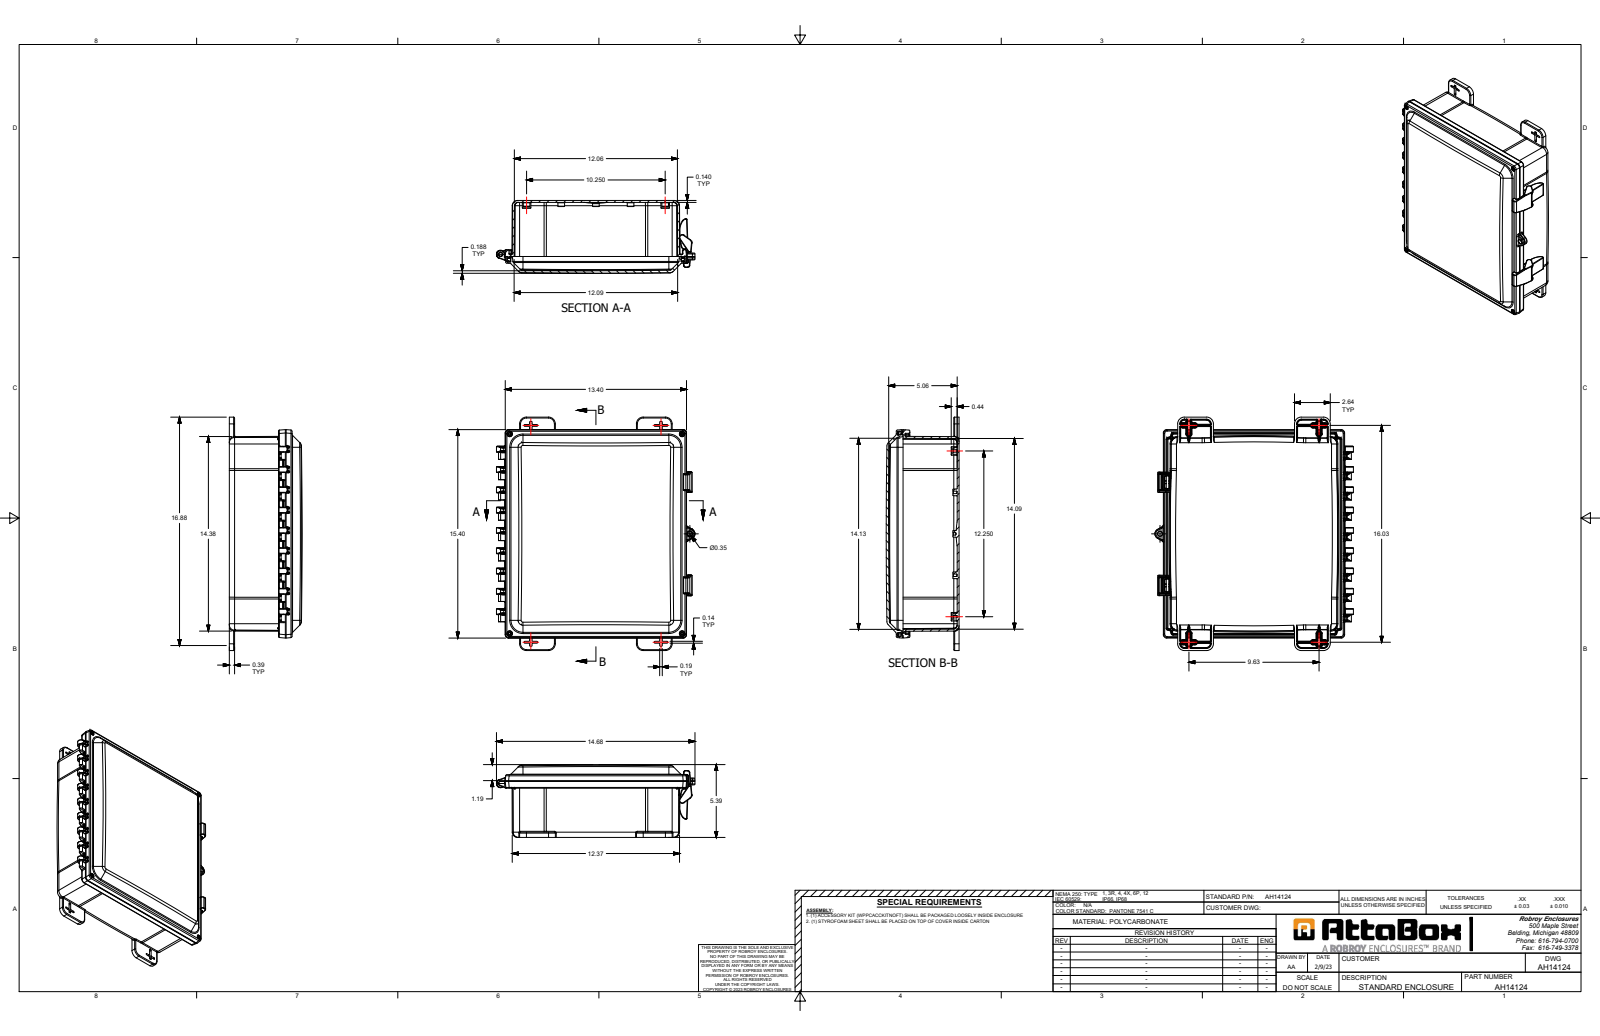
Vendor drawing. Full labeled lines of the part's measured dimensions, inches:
Part name (STEP PRODUCT): AH14124C
STEP written by: SolidWorks 2023 (AUTOMOTIVE_DESIGN)
Units: inches
Bodies: 6 solids, 1306 faces (449 planar, 451 cylindrical, 406 other)
Overall size (bounding box): 17.25 × 14.676 × 5.388
Volume: 123.2 in³ · Surface area: 1 453 in²
Round holes (diameter × count): ⌀0.187 ×21, ⌀0.195 ×4, ⌀0.25 ×4, ⌀0.296 ×4, ⌀0.39 ×4, ⌀0.327 ×1, ⌀0.375 ×1, ⌀0.45 ×1
Round bosses / shafts (diameter × count): ⌀0.487 ×21, ⌀0.625 ×4, ⌀0.2 ×2, ⌀0.313 ×1
Partial cylindrical surfaces — rounded edges, fillets, slot ends (radius × count): R0.035 ×194, R0.065 ×23, R0.01 ×22, R0.5 ×8, R5.14 ×8, R0.09 ×4, R0.25 ×4, R0.36 ×4
Main face-to-face distances: 0.14, 4.14, 4, 12.247, 0.5, 0.191, 14.243, 3.64, 3.5, 0.124
Hole centre spacings: 5.97, 2.563, 3.993, 3.993, 6.639, 8.275, 9.538, 5.125
